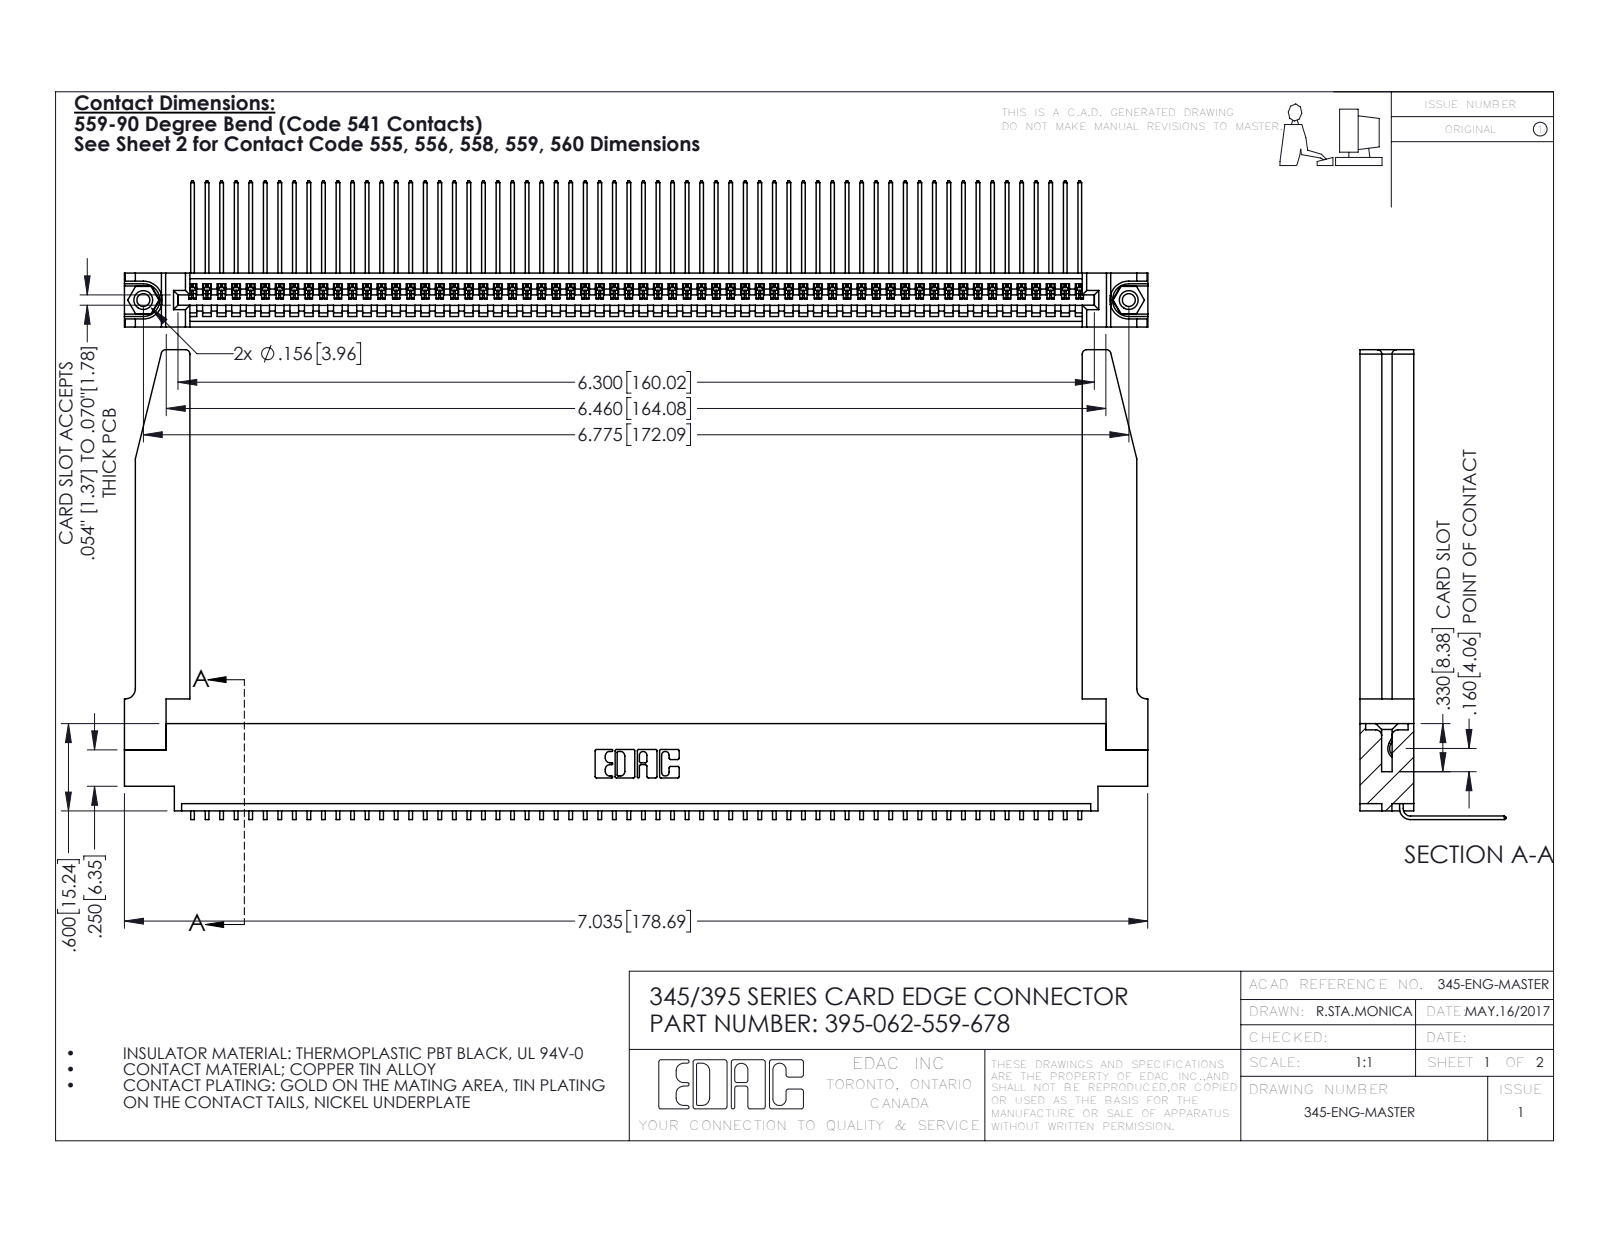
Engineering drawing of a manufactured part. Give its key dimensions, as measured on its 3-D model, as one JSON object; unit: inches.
{"part_name": "345 Part_0.170 Offset - 0.156 Dia-TH; 345-292-001_558 559 Tail - 1; 395-062-559-678; 345-220-078_345-220-078 (+1 more)", "step_written_by": "SolidWorks 2016 (CONFIG_CONTROL_DESIGN)", "units": "inches", "bodies": {"solids": 67, "faces": 4084, "planar": 2830, "cylindrical": 1202, "other": 52}, "overall_size": [7.036, 3.229, 1.005], "volume_in3": 1.526, "surface_area_in2": 48.6, "round_holes": [[0.089, 2], [0.125, 2], [0.156, 2], [0.064, 1]], "round_bosses_or_shafts": [[0.155, 2]], "partial_cylinders_radius": [[0.006, 124], [0.01, 22], [0.03, 8], [0.007, 6], [0.031, 6], [0.026, 3], [0.031, 2], [0.04, 2]], "face_to_face_distances": [0.37, 0.072, 0.298, 0.098, 0.272, 0.025, 0.2, 0.225, 0.148, 0.15], "hole_center_spacings": [0.27, 6.539, 6.775]}
